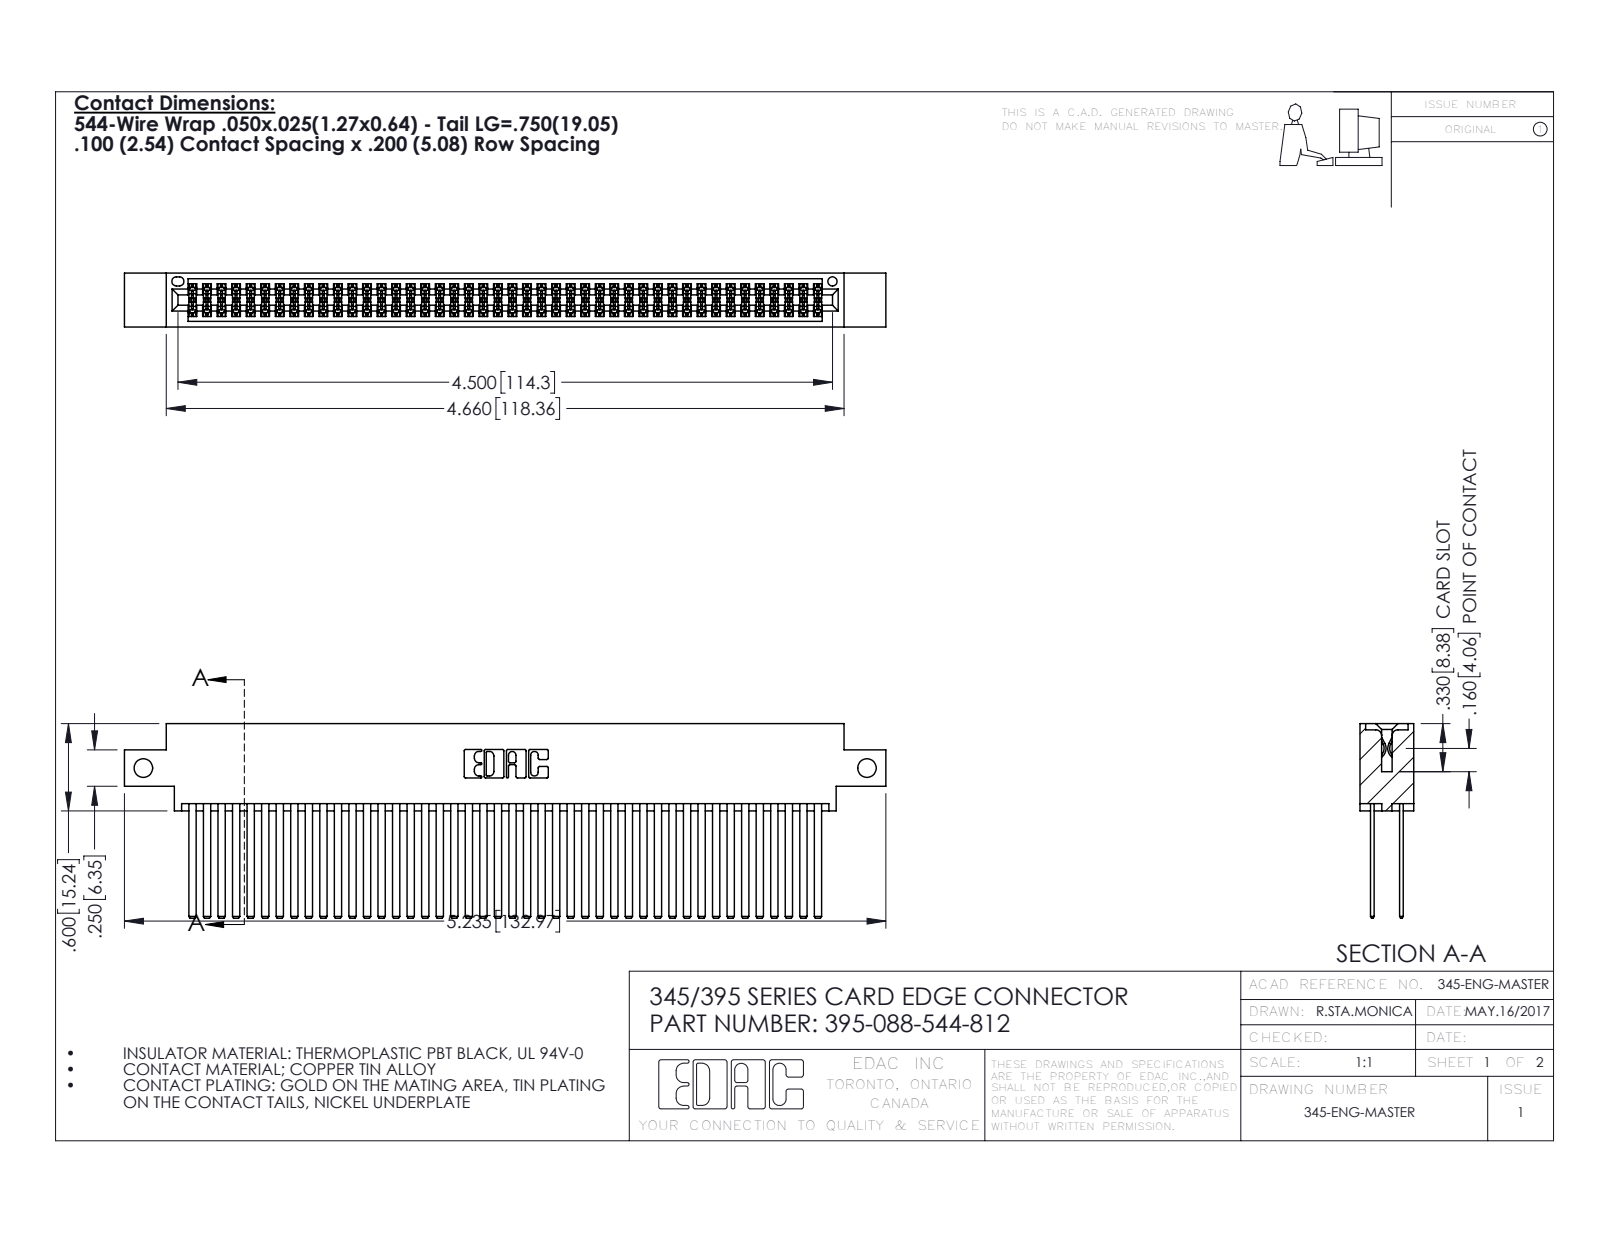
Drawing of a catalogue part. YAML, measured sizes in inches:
part_name: "345 Part_0.170 Offset - Side Mount; 345-292-001_345-293-144; 395-088-544-812"
step_written_by: "SolidWorks 2016 (CONFIG_CONTROL_DESIGN)"
units: inches
bodies: {solids: 89, faces: 4002, planar: 2636, cylindrical: 1366, other: 0}
overall_size: [5.235, 1.337, 0.37]
volume: 0.852
surface_area: 37.68
round_holes:
  - {diameter: 0.128, count: 2}
  - {diameter: 0.064, count: 1}
partial_cylinders:
  - {radius: 0.006, count: 132}
  - {radius: 0.01, count: 22}
  - {radius: 0.007, count: 6}
  - {radius: 0.031, count: 6}
  - {radius: 0.026, count: 3}
  - {radius: 0.014, count: 2}
  - {radius: 0.019, count: 2}
  - {radius: 0.022, count: 2}
face_to_face_distances: [0.2, 0.025, 0.298, 0.072, 0.098, 0.272, 0.225, 0.175, 0.37, 0.15]
hole_center_spacings: [4.975]
